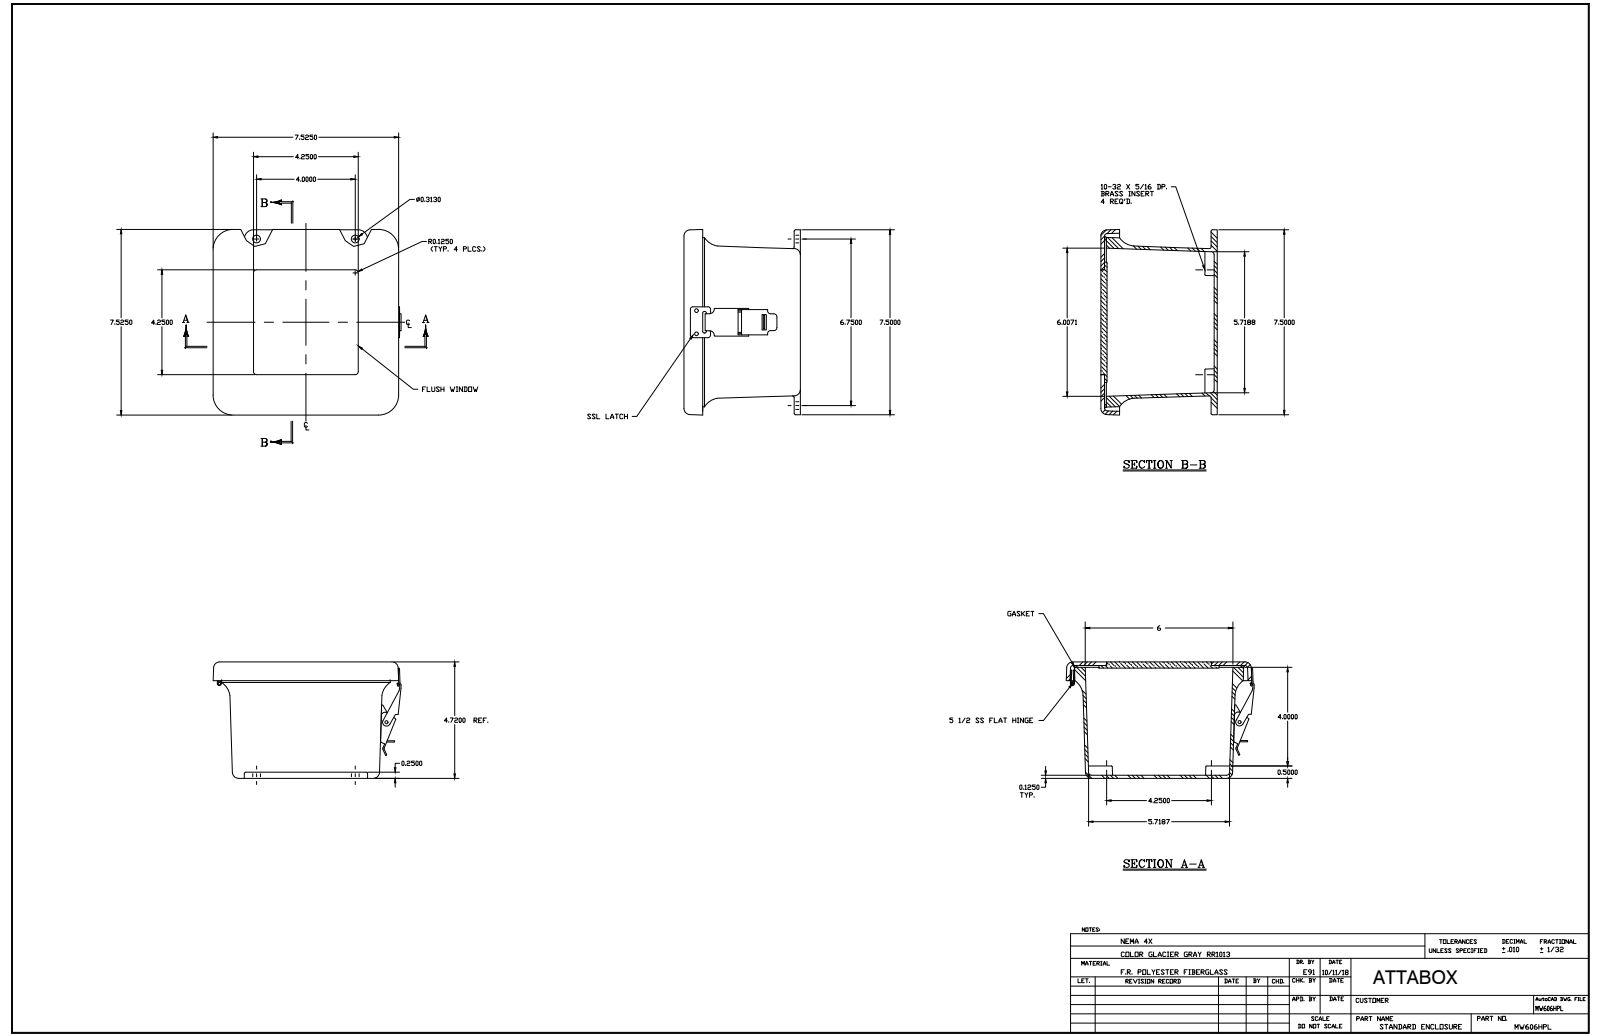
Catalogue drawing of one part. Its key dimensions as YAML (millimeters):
part_name: "MW606HPL"
step_written_by: "SolidWorks 2018 (AUTOMOTIVE_DESIGN)"
units: millimeters
bodies: {solids: 26, faces: 658, planar: 264, cylindrical: 270, other: 124}
overall_size: [193.4, 191.1, 122.5]
volume: 664500
surface_area: 345500
round_holes:
  - {diameter: 3.6, count: 11}
  - {diameter: 3.3, count: 5}
  - {diameter: 3.9, count: 5}
  - {diameter: 2.6, count: 4}
  - {diameter: 4, count: 4}
  - {diameter: 5.5, count: 4}
  - {diameter: 3.3, count: 2}
  - {diameter: 3.4, count: 2}
  - {diameter: 2.2, count: 1}
  - {diameter: 2.2, count: 1}
  - {diameter: 9.5, count: 1}
round_bosses_or_shafts:
  - {diameter: 6.4, count: 5}
  - {diameter: 3.2, count: 5}
  - {diameter: 6.9, count: 4}
  - {diameter: 3.2, count: 4}
  - {diameter: 7.6, count: 1}
  - {diameter: 4.3, count: 1}
  - {diameter: 3.9, count: 1}
  - {diameter: 3.9, count: 1}
partial_cylinders:
  - {radius: 0.8, count: 20}
  - {radius: 3.2, count: 16}
  - {radius: 6.4, count: 16}
  - {radius: 0.4, count: 12}
  - {radius: 1.1, count: 8}
  - {radius: 0.8, count: 6}
  - {radius: 0.6, count: 5}
  - {radius: 5.1, count: 5}
face_to_face_distances: [3.7, 118.8, 122.5, 6.4, 116.2, 3.2, 115.6, 119.4, 113, 2.6]
hole_center_spacings: [134.8, 23.8, 34.8, 63.5, 108, 157.1, 187.5, 19.1]
